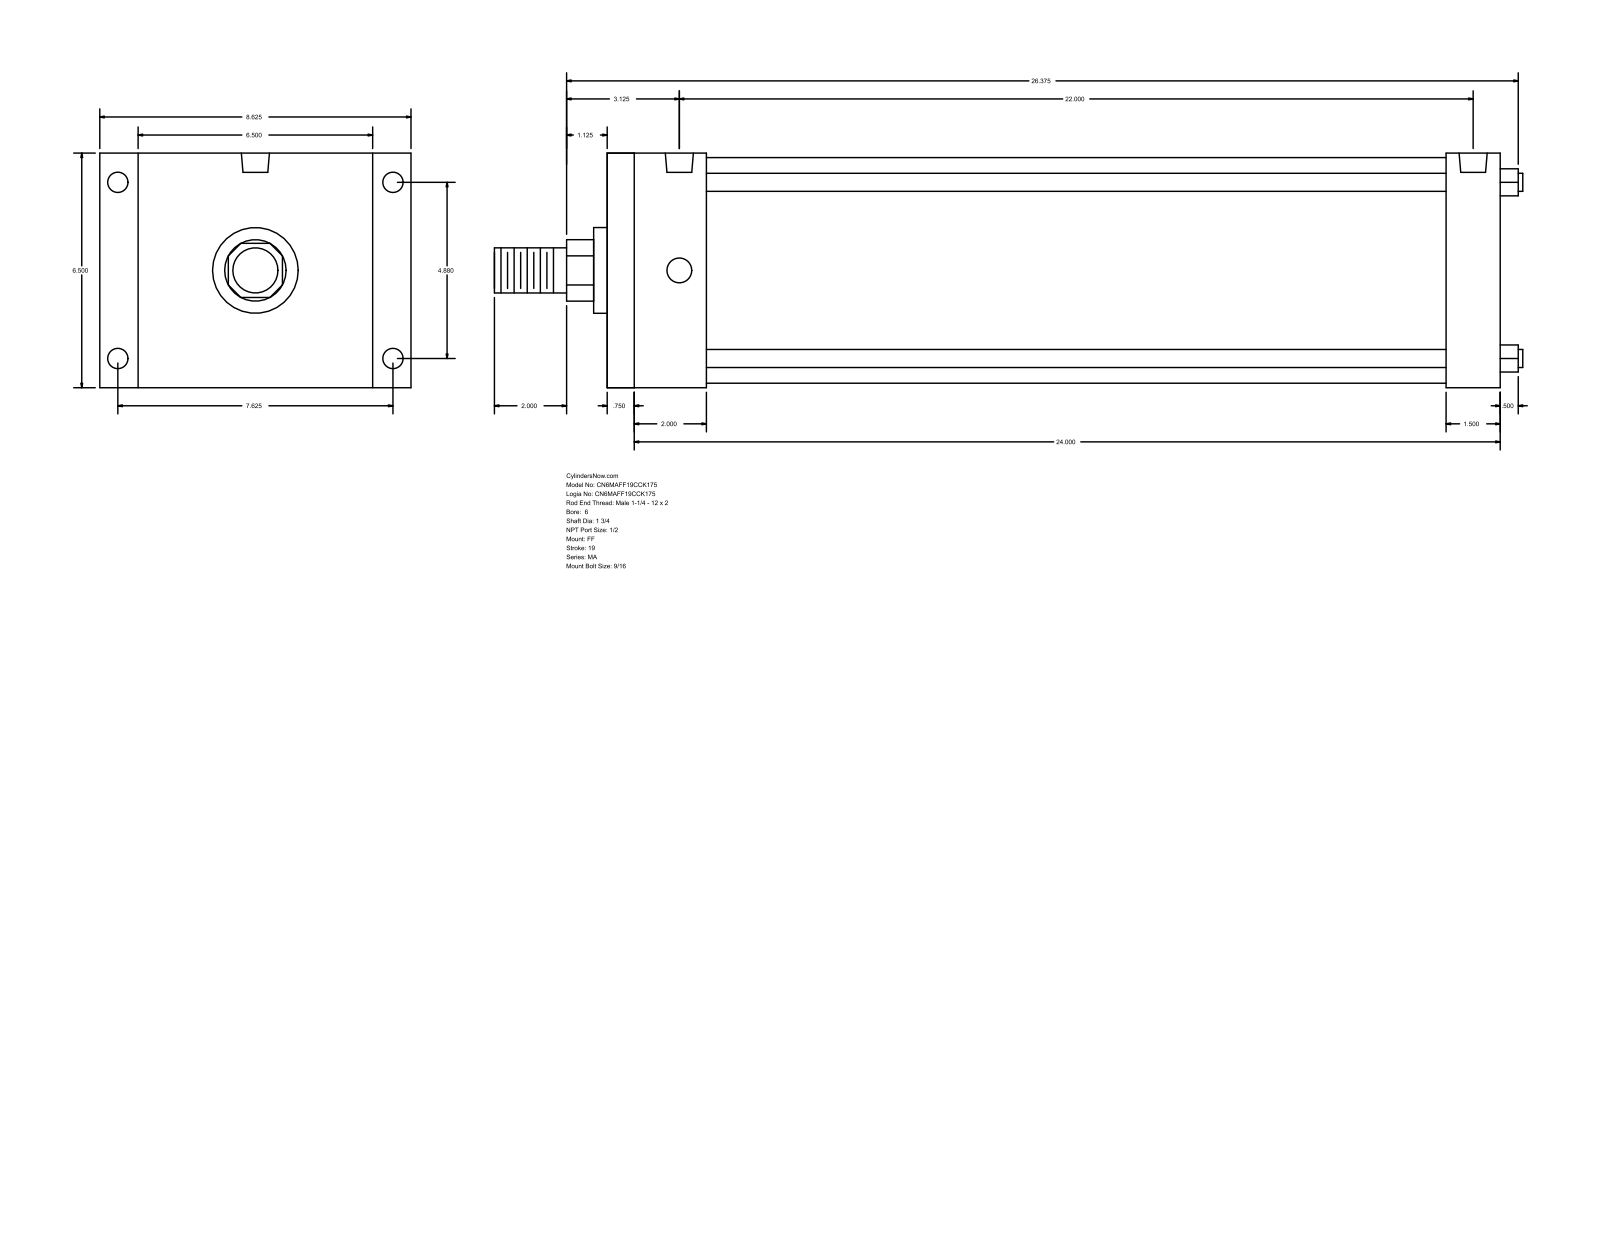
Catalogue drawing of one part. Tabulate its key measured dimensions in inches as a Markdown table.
| quantity | value |
| --- | --- |
| part name | MA_FF__0600_1.75 |
| STEP written by | GSSL Pune (CONFIG_CONTROL_DESIGN) |
| units | inches |
| bodies | 0 solids, 92 faces (64 planar, 28 cylindrical, 0 other) |
| overall size | 28.5 × 8.625 × 6.5 |
| round holes (diameter × count) | 0.563 × 4, 0.687 × 4, 0.778 × 2 |
| round bosses / shafts (diameter × count) | 0.5 × 4, 6.25 × 1, 2.375 × 1, 1.75 × 1, 1.25 × 1 |
| partial cylindrical surfaces (radius × count) | 0.852 × 1 |
| main face-to-face distances | 6.5, 24.75, 0.75, 24, 2, 2.75, 22.5, 22, 23.25, 20.5 |
| hole center spacings | 4.88, 7.625, 9.053, 22 |
